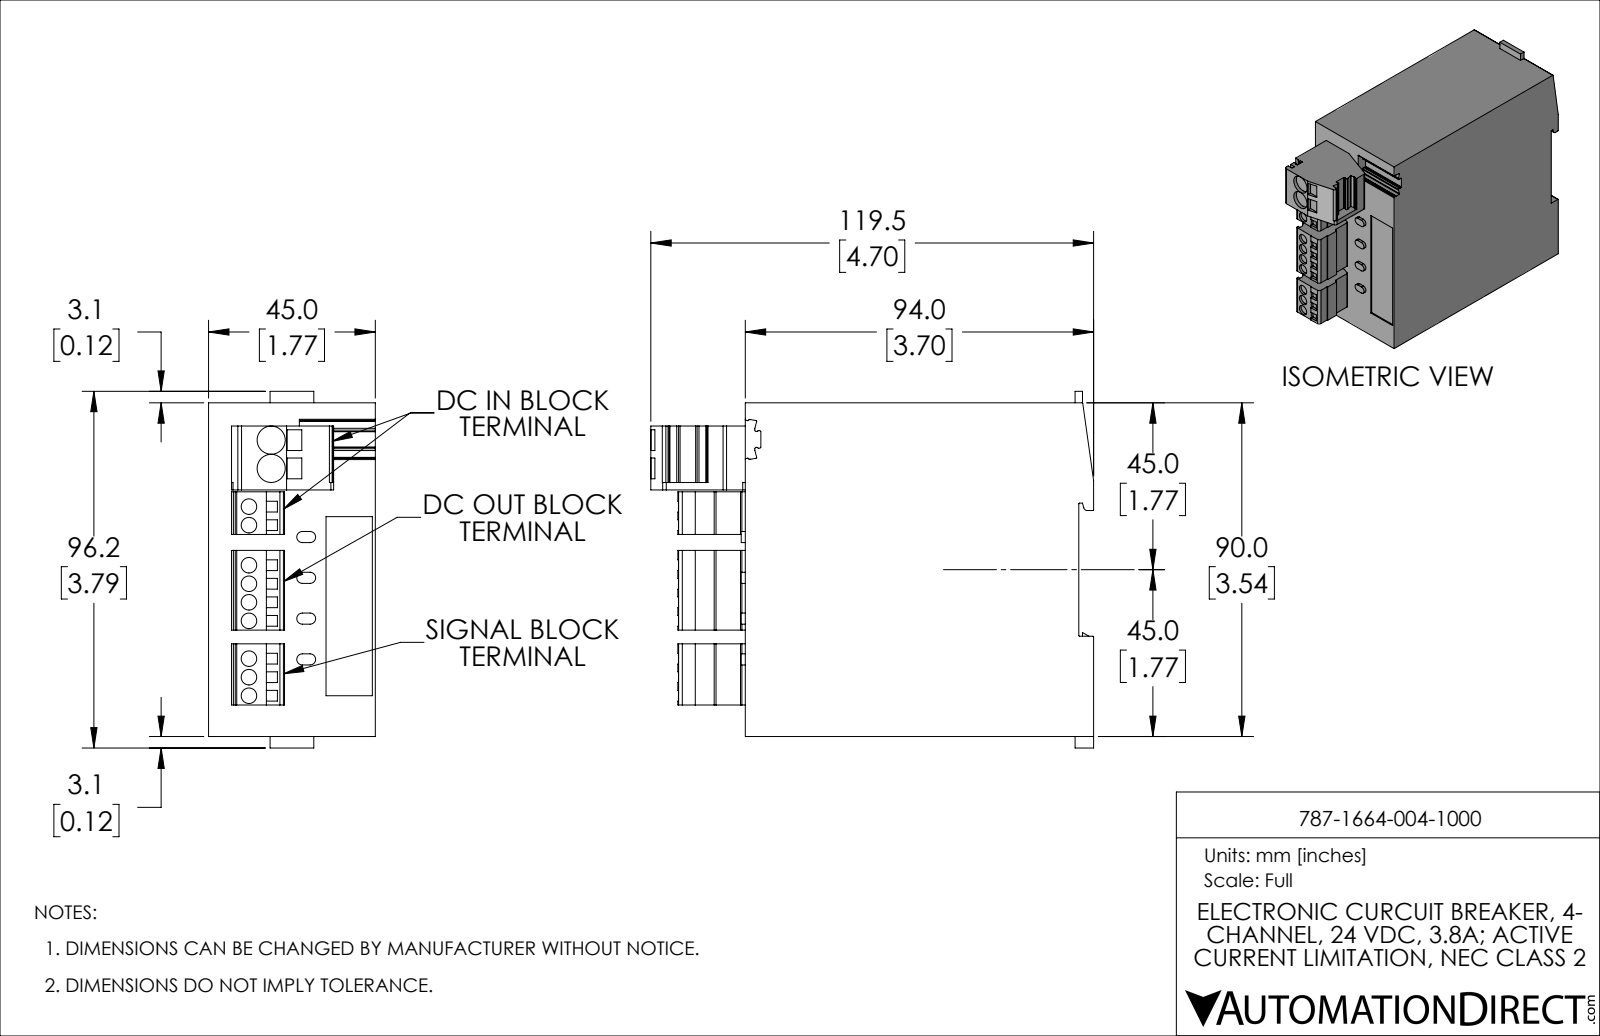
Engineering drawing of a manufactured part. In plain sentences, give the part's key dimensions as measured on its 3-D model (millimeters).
The part is named "787-1664/004-1000". Its 3-D file was written by "PARTsolutions (CONFIG_CONTROL_DESIGN)". It is 1 solid with 328 faces: 248 planar, 80 cylindrical and 0 other. Overall it measures 119.5 by 96.2 by 45 millimeters. Its volume is 393 125 cubic millimeters and its surface area 41 275 square millimeters. Round holes: 9 of diameter 4.2, 2 of diameter 7.6. Partial cylindrical surfaces (rounded edges, fillets, slot ends): 25 of radius 0.2, 8 of radius 1.5, 7 of radius 1, 6 of radius 0.4, 4 of radius 0.3, 4 of radius 0.49, 1 of radius 2. The main face-to-face distances are 45, 90, 4, 94, 0.5, 38.8, 6.2, 23.5, 66.5, 16.5. The hole center spacings are 5, 10, 20.2, 25.2, 15.2, 15.8, 20.8, 25.8.
